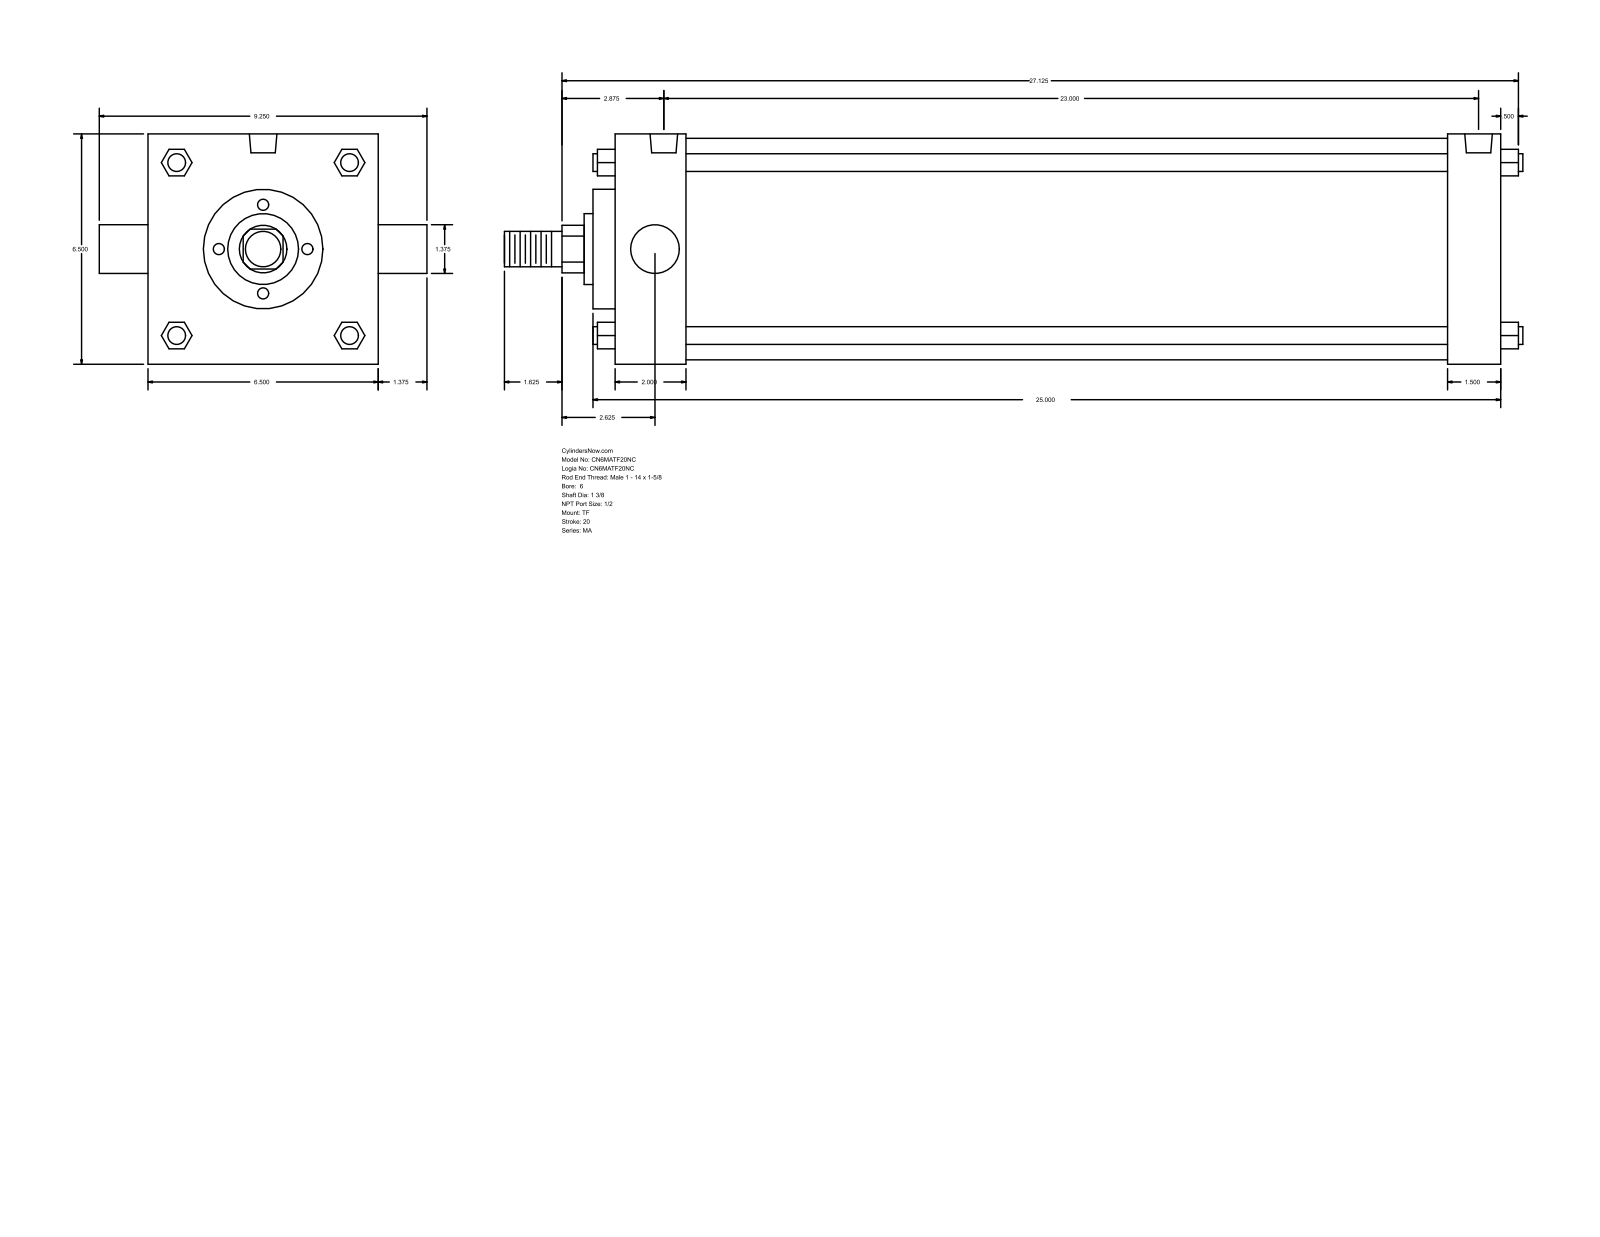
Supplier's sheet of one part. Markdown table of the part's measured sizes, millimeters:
| quantity | value |
| --- | --- |
| part name | MA_TF__0600_1.375 |
| STEP written by | GSSL Pune (CONFIG_CONTROL_DESIGN) |
| units | millimeters |
| bodies | 0 solids, 122 faces (93 planar, 29 cylindrical, 0 other) |
| overall size | 730.25 × 234.95 × 165.1 |
| round holes (diameter × count) | 17.46 × 3, 19.77 × 2 |
| round bosses / shafts (diameter × count) | 12.7 × 4, 34.92 × 2, 158.75 × 1, 85.72 × 1, 50.8 × 1, 25.4 × 1 |
| partial cylindrical surfaces (radius × count) | 17.06 × 1 |
| main face-to-face distances | 165.1, 638.17, 38.1, 50.8, 587.37, 600.07, 549.27, 66.67, 15.87, 615.94 |
| hole center spacings | 3.18, 584.2, 587.38 |
